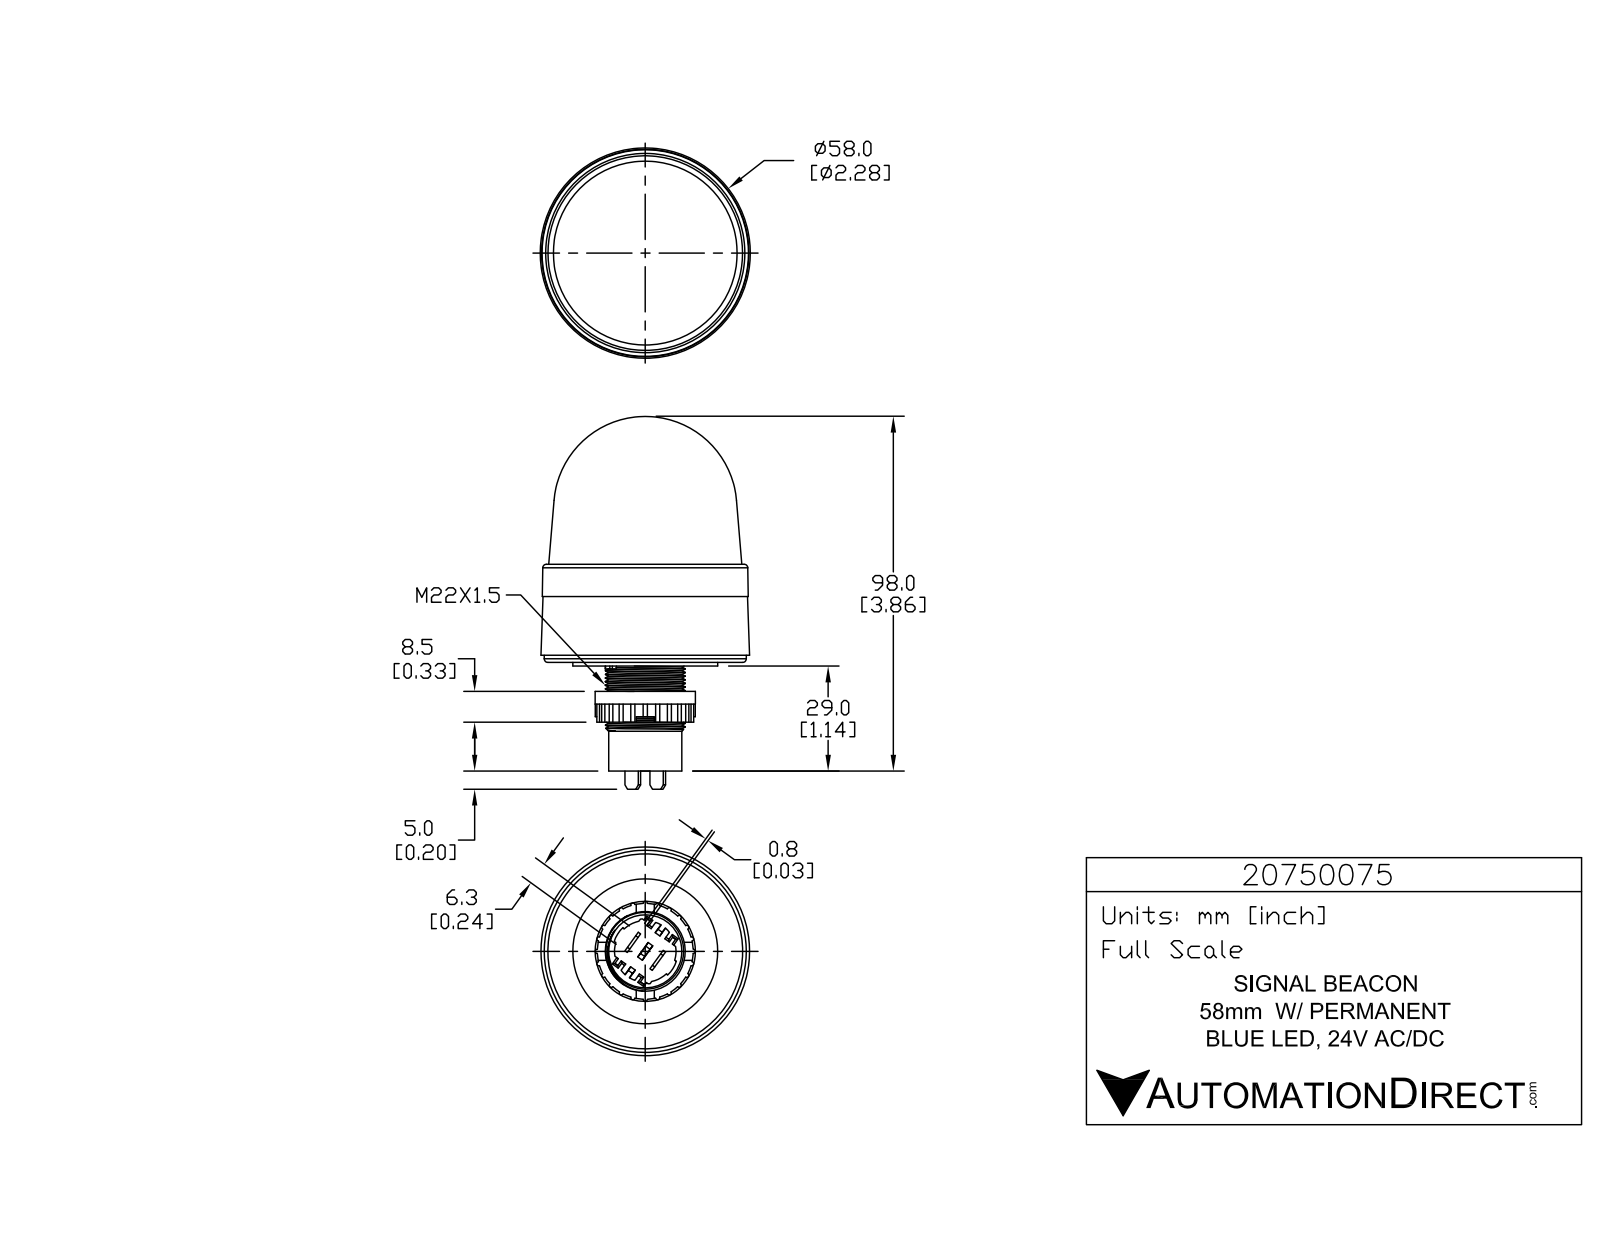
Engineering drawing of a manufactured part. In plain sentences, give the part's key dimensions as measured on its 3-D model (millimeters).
The part is named "20750075". Its 3-D file was written by "SolidWorks 2015 (AUTOMOTIVE_DESIGN)". It is 1 solid with 266 faces: 119 planar, 120 cylindrical and 27 other. Overall it measures 102.9 by 57.6 by 57.6 millimeters. Its volume is 147 700 cubic millimeters and its surface area 20 030 square millimeters. Round holes: 1 of diameter 23. Round bosses or shafts: 1 of diameter 55.8, 1 of diameter 40, 1 of diameter 27.7, 1 of diameter 22, 1 of diameter 20.2. Partial cylindrical surfaces (rounded edges, fillets, slot ends): 24 of radius 0.6, 2 of radius 0.5, 1 of radius 8.5, 1 of radius 9, 1 of radius 13.3. The main face-to-face distances are 1, 7, 3, 29, 8.5, 8, 27, 19, 26, 18.5.
